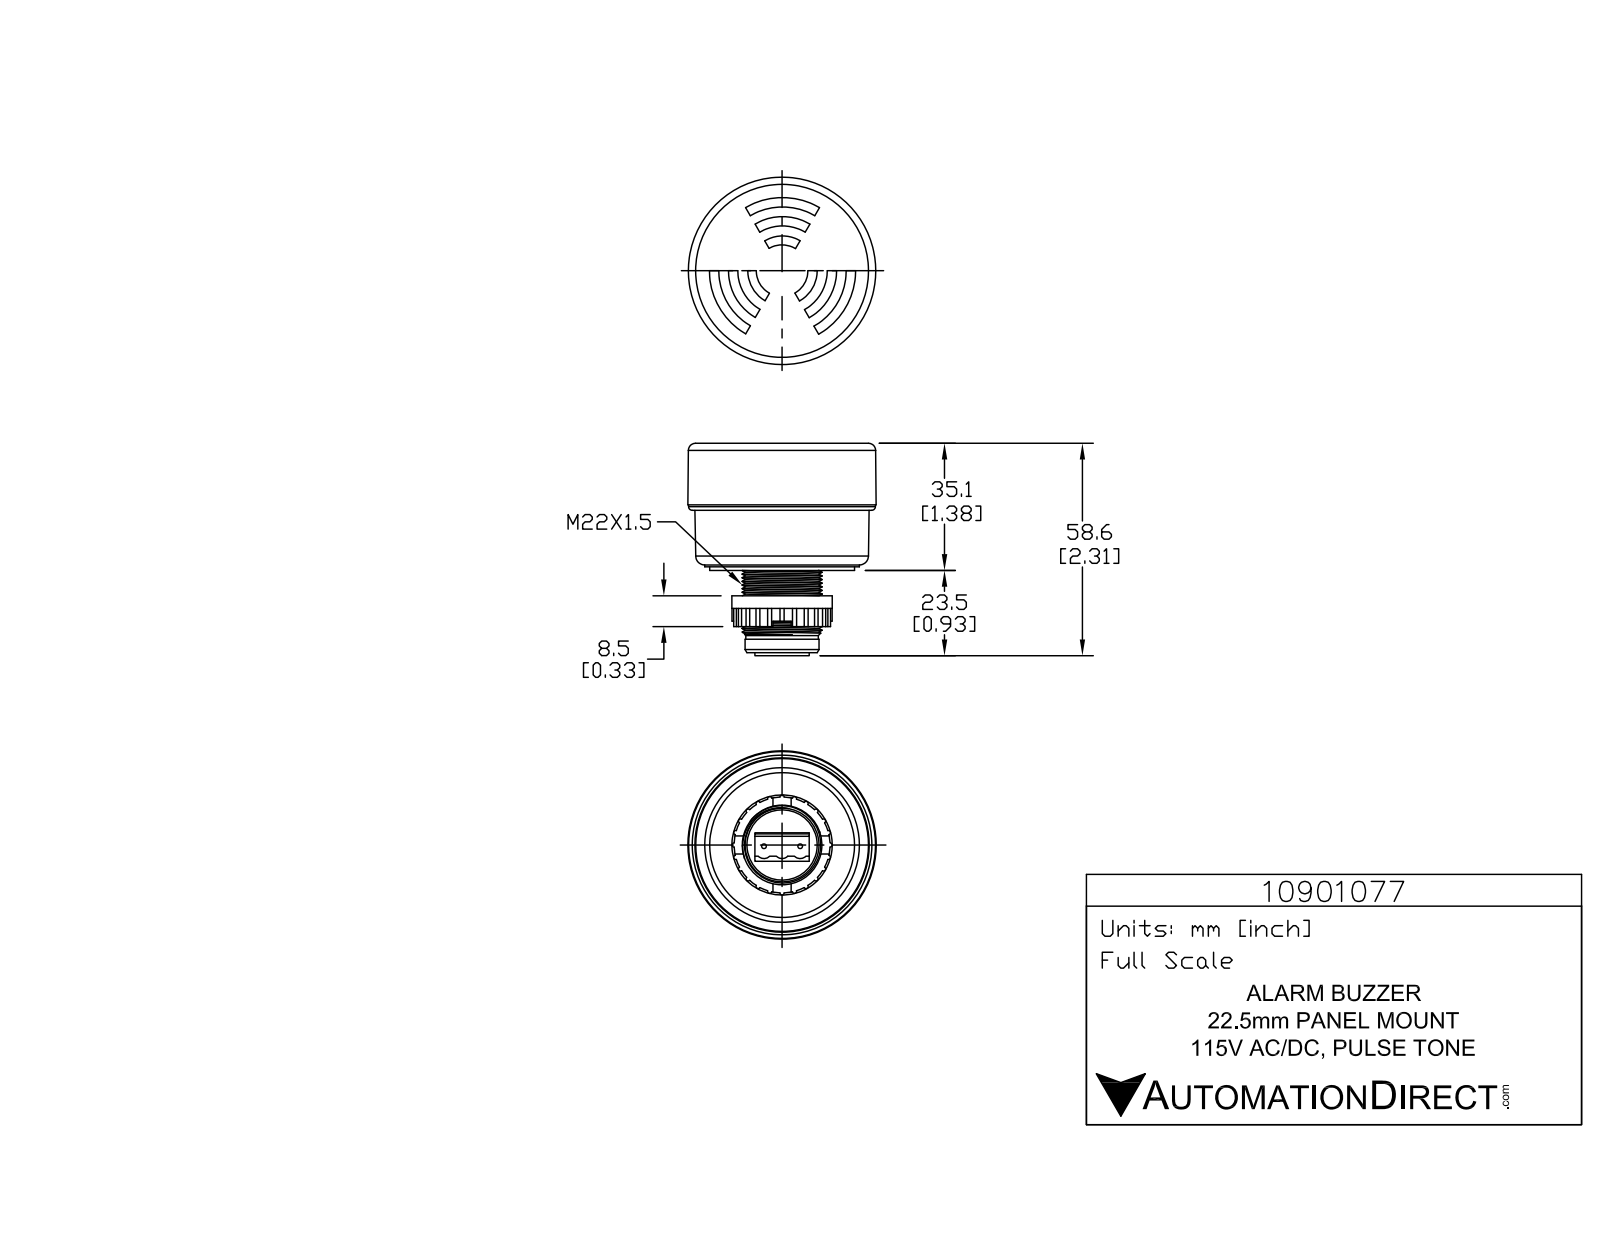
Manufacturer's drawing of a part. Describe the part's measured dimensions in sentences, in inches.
The part is named "10901077". Its 3-D file was written by "SolidWorks 2017 (AUTOMOTIVE_DESIGN)". It is 1 solid with 1180 faces: 766 planar, 311 cylindrical and 103 other. Overall it measures 2.309 by 2.054 by 2.05 inches. Its volume is 4.656 cubic inches and its surface area 22.8 square inches. Round holes: 4 of diameter 0.039, 1 of diameter 0.906. Round bosses or shafts: 4 of diameter 0.226, 4 of diameter 0.056, 2 of diameter 0.051, 1 of diameter 2.031, 1 of diameter 1.681, 1 of diameter 1.575, 1 of diameter 1.091, 1 of diameter 0.866. Partial cylindrical surfaces (rounded edges, fillets, slot ends): 24 of radius 0.023, 8 of radius 0.008, 8 of radius 0.008, 8 of radius 0.008, 8 of radius 0.131, 4 of radius 0.004, 4 of radius 0.005, 4 of radius 0.008. The main face-to-face distances are 1.374, 0.276, 1.65, 0.039, 0.315, 1.335, 0.898, 0.937, 0.622, 2.272. The hole center spacings are 0.242.
